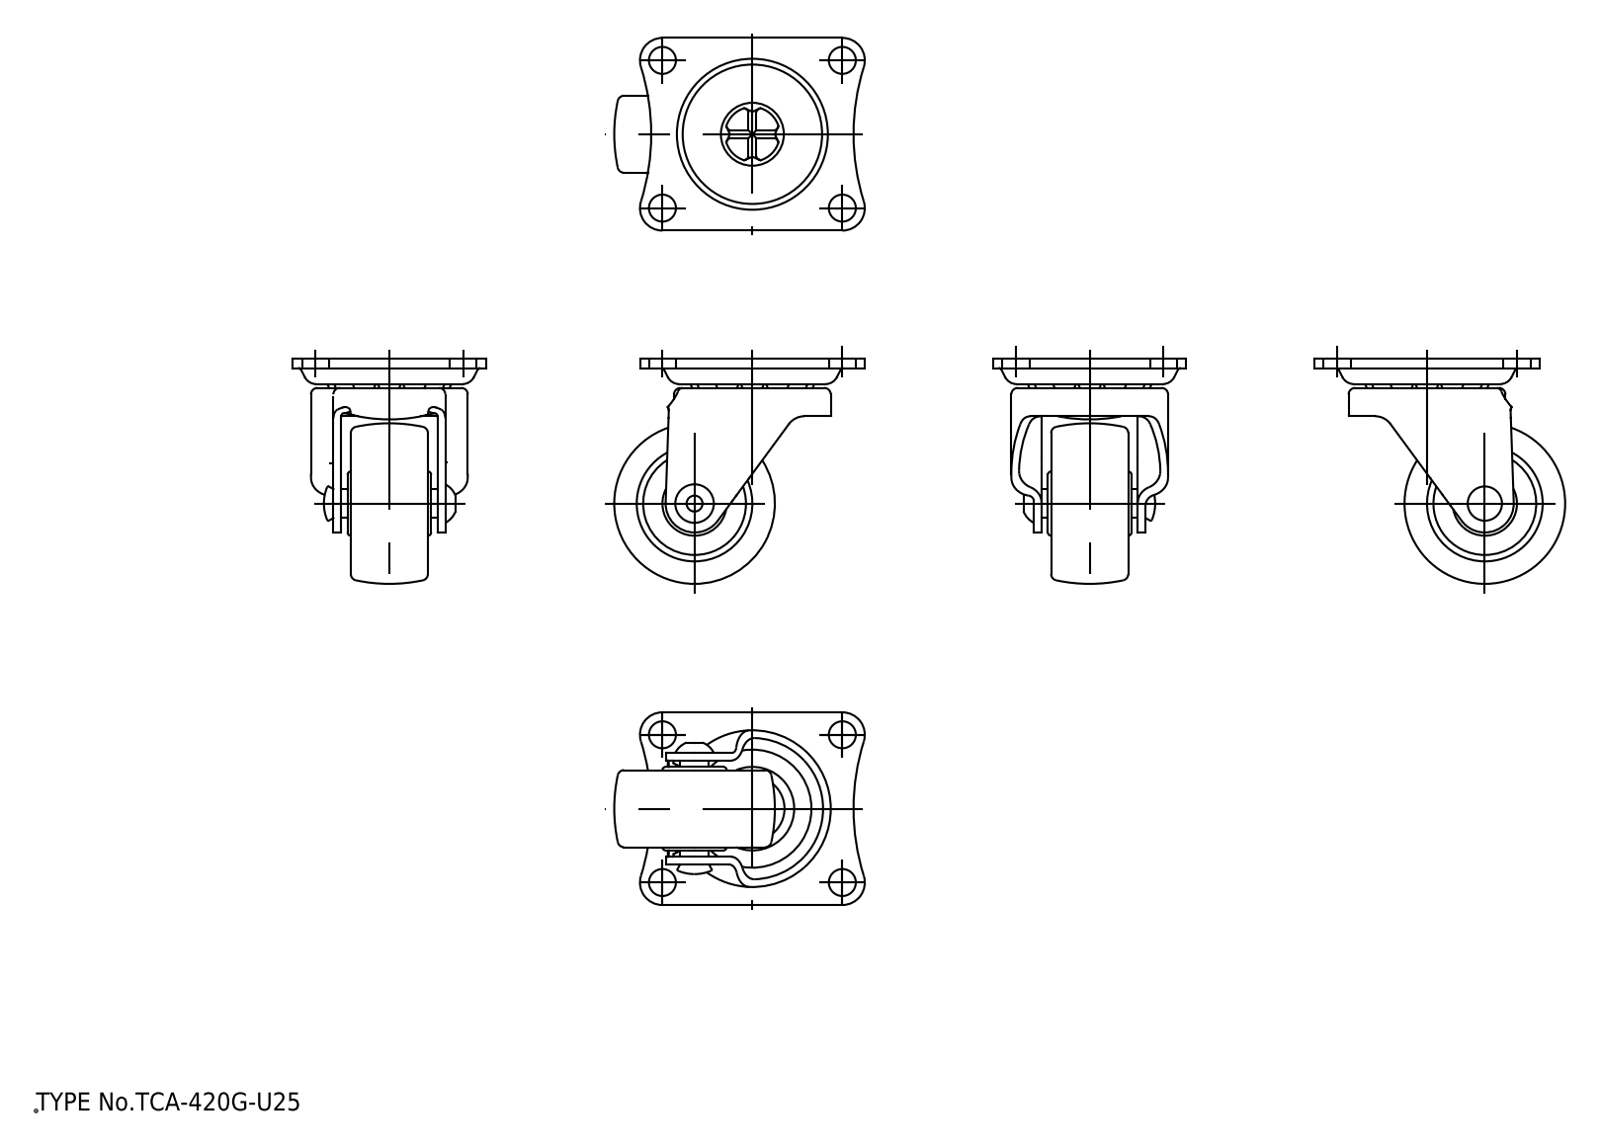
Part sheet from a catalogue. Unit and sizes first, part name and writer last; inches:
Units: inches
Overall size (bounding box): 1.535 × 1.378 × 1.181
Round holes (diameter × count): ⌀0.165 ×4, ⌀0.177 ×1, ⌀0.276 ×1, ⌀0.866 ×1
Round bosses / shafts (diameter × count): ⌀0.394 ×2, ⌀0.961 ×1
Partial cylindrical surfaces — rounded edges, fillets, slot ends (radius × count): R0.02 ×10, R0.079 ×5, R0.138 ×4, R0.118 ×3, R0.039 ×2, R1.378 ×2, R0.167 ×1, R0.177 ×1
Main face-to-face distances: 0.047, 0.055, 0.039, 0.059, 0.492, 0.098, 0.169, 0.224, 0.433, 0.122
Hole centre spacings: 0.713, 0.906, 1.102, 1.427
Volume: 0.55 in³ · Surface area: 12.57 in²
Bodies: 5 solids, 237 faces (62 planar, 69 cylindrical, 106 other)
Part name (STEP PRODUCT): wheel; mounting plate; main shaft; axle
STEP written by: spGate 19.8.4 (****-****-****-****) (AUTOMOTIVE_DESIGN)
